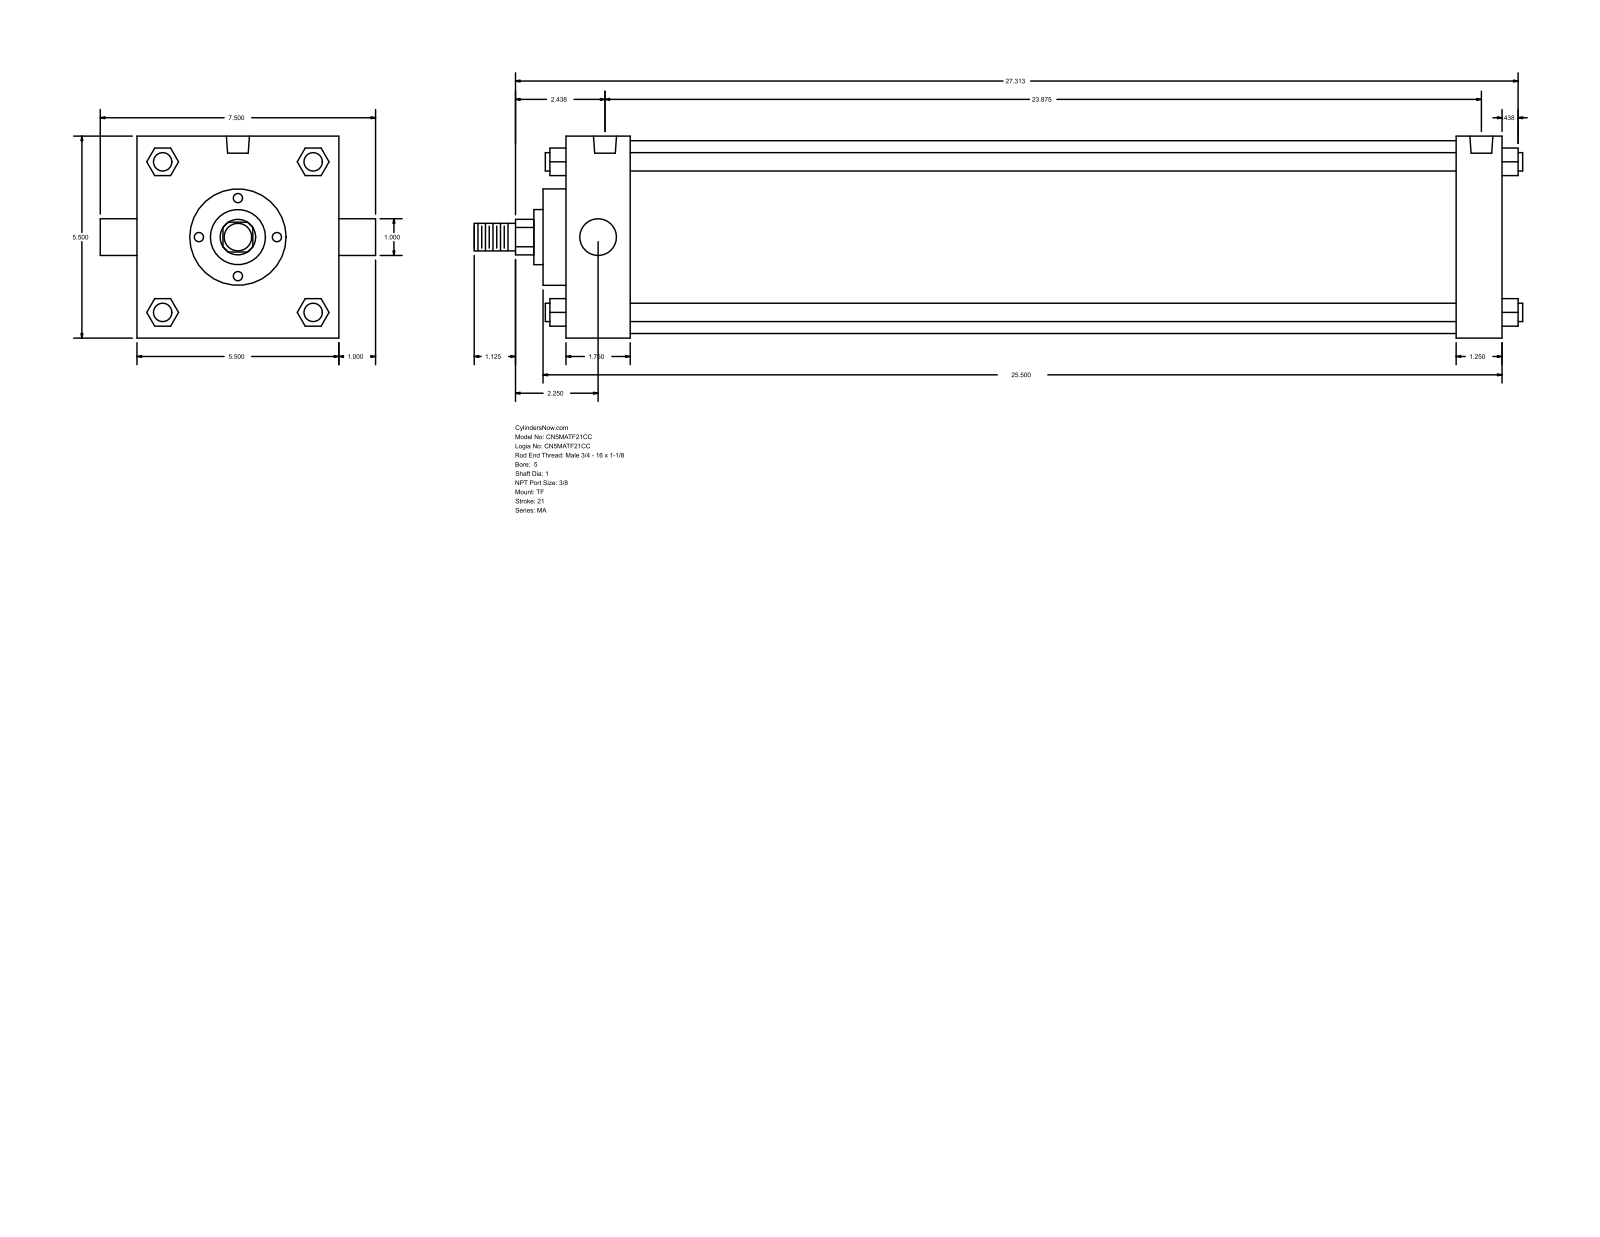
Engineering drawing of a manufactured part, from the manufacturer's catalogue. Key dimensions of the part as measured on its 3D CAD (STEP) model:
Part name (STEP PRODUCT): MA_TF__0500_1
STEP written by: GSSL Pune (CONFIG_CONTROL_DESIGN)
Units: millimetres
Bodies: 0 solids, 122 faces (93 planar, 29 cylindrical, 0 other)
Overall size (bounding box): 725.49 × 190.5 × 139.7
Round holes (diameter × count): ⌀11.11 ×3, ⌀15.93 ×2
Round bosses / shafts (diameter × count): ⌀12.7 ×4, ⌀25.4 ×2, ⌀133.35 ×1, ⌀66.67 ×1, ⌀38.1 ×1, ⌀19.05 ×1
Partial cylindrical surfaces — rounded edges, fillets, slot ends (radius × count): R12.29 ×1
Main face-to-face distances: 139.7, 647.7, 615.96, 31.74, 44.46, 571.5, 603.24, 15.87, 60.33, 631.83
Hole centre spacings: 4.76, 601.67, 596.91, 606.43
